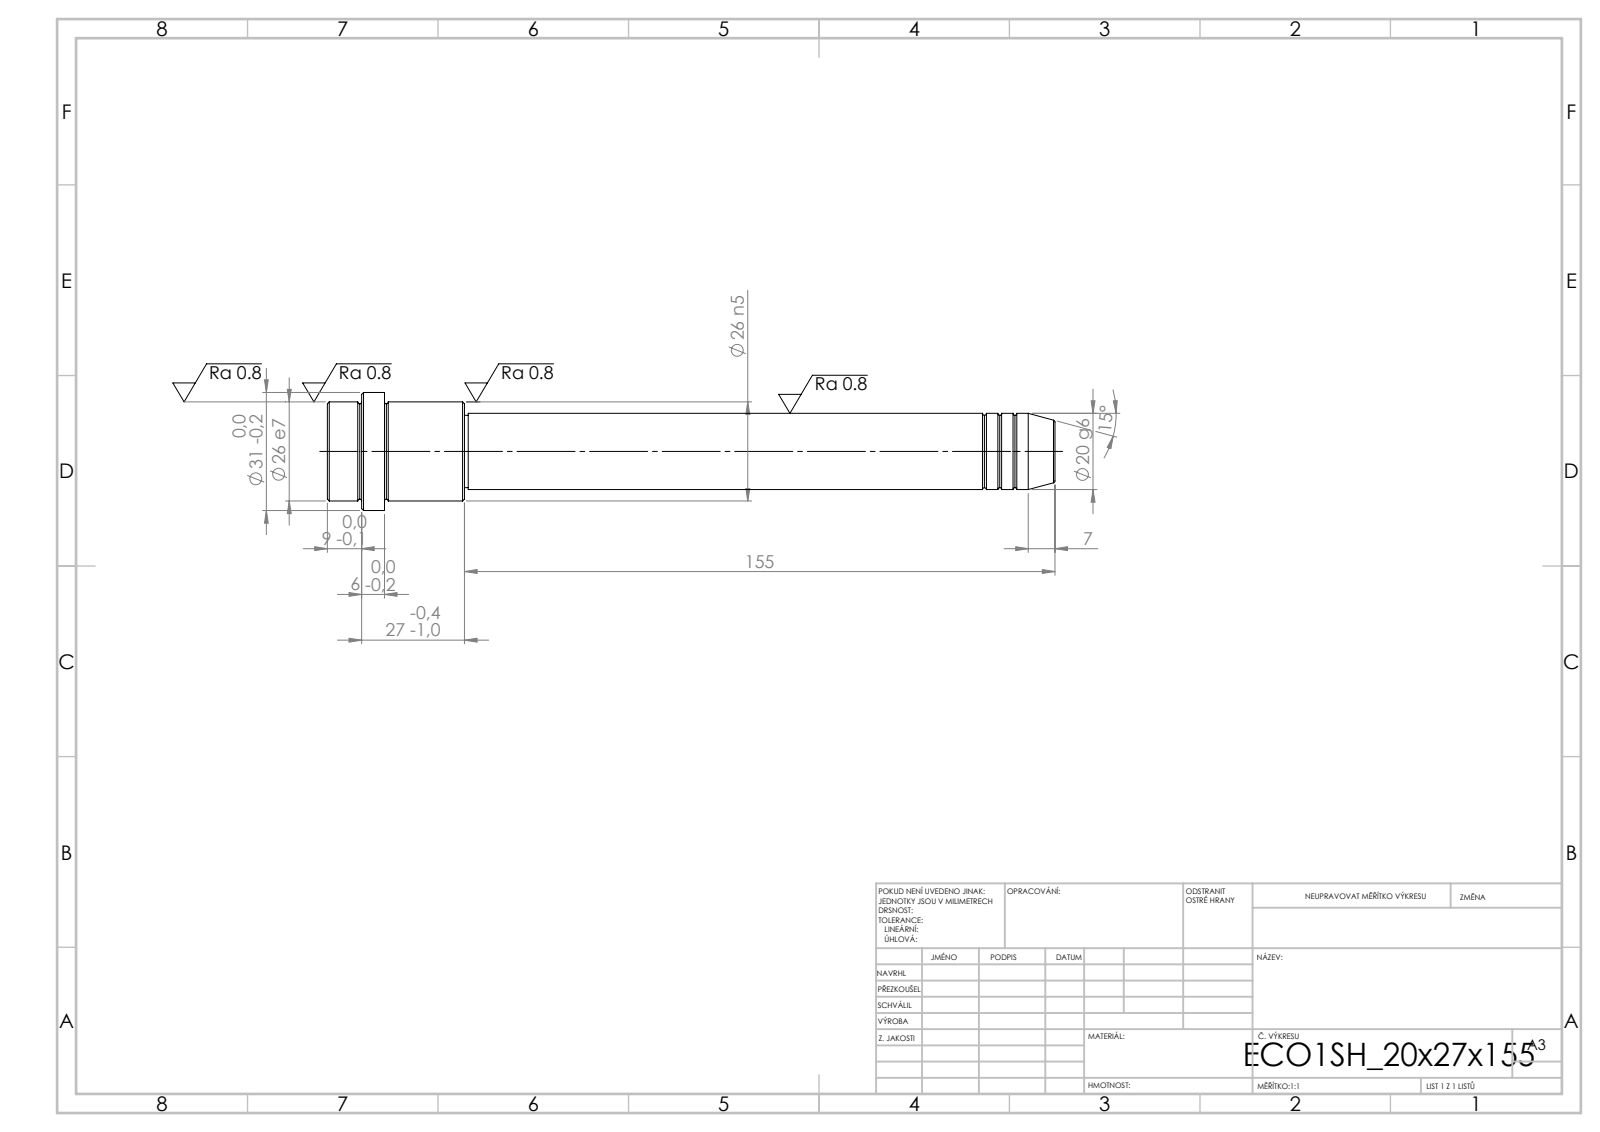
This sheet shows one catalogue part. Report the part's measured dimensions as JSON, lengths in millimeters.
{"step_written_by": "SolidWorks 2019 (CONFIG_CONTROL_DESIGN)", "units": "millimeters", "bodies": {"solids": 1, "faces": 52, "planar": 6, "cylindrical": 16, "other": 30}, "overall_size": [191, 31, 31], "volume_mm3": 68565, "surface_area_mm2": 14309, "round_bosses_or_shafts": [[31, 1], [26, 1], [20, 1], [19, 1]], "face_to_face_distances": [15, 21, 36, 155, 176, 191, 182, 27, 6, 9]}
